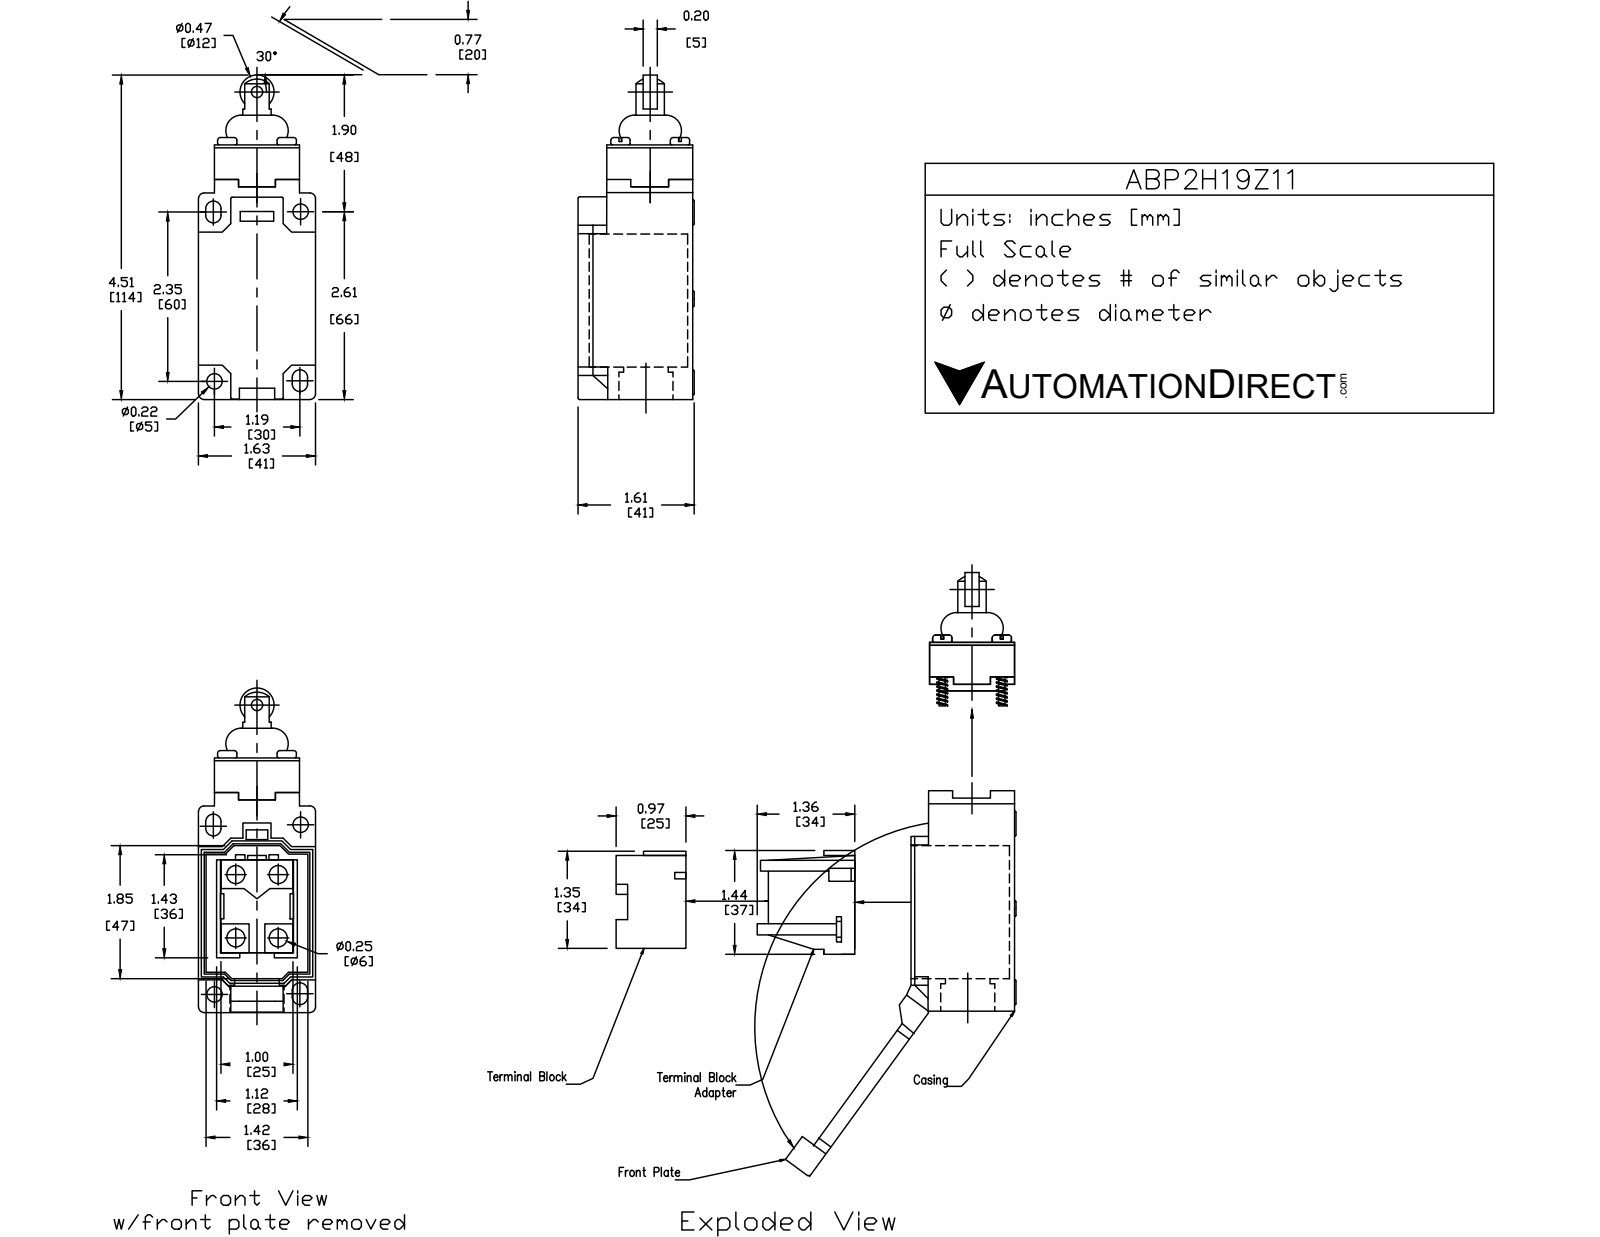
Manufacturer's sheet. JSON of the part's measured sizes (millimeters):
{"part_name": "ABP2H19Z11", "step_written_by": "SolidWorks 2017 (AUTOMOTIVE_DESIGN)", "units": "millimeters", "bodies": {"solids": 4, "faces": 188, "planar": 86, "cylindrical": 76, "other": 26}, "overall_size": [116.7, 41, 40.3], "volume_mm3": 127500, "surface_area_mm2": 25070, "round_holes": [[5.4, 2], [10.1, 1], [17, 1], [19, 1], [20.5, 1]], "round_bosses_or_shafts": [[9, 4], [7, 4], [20, 1], [12, 1], [10, 1]], "partial_cylinders_radius": [[0.5, 16], [0.6, 4], [2, 4], [2.7, 4], [11.5, 1], [12, 1]], "face_to_face_distances": [41, 39.8, 30, 75.5, 9.8, 5.5, 35.5, 2.5, 78, 12], "hole_center_spacings": [1.5, 67.1]}
